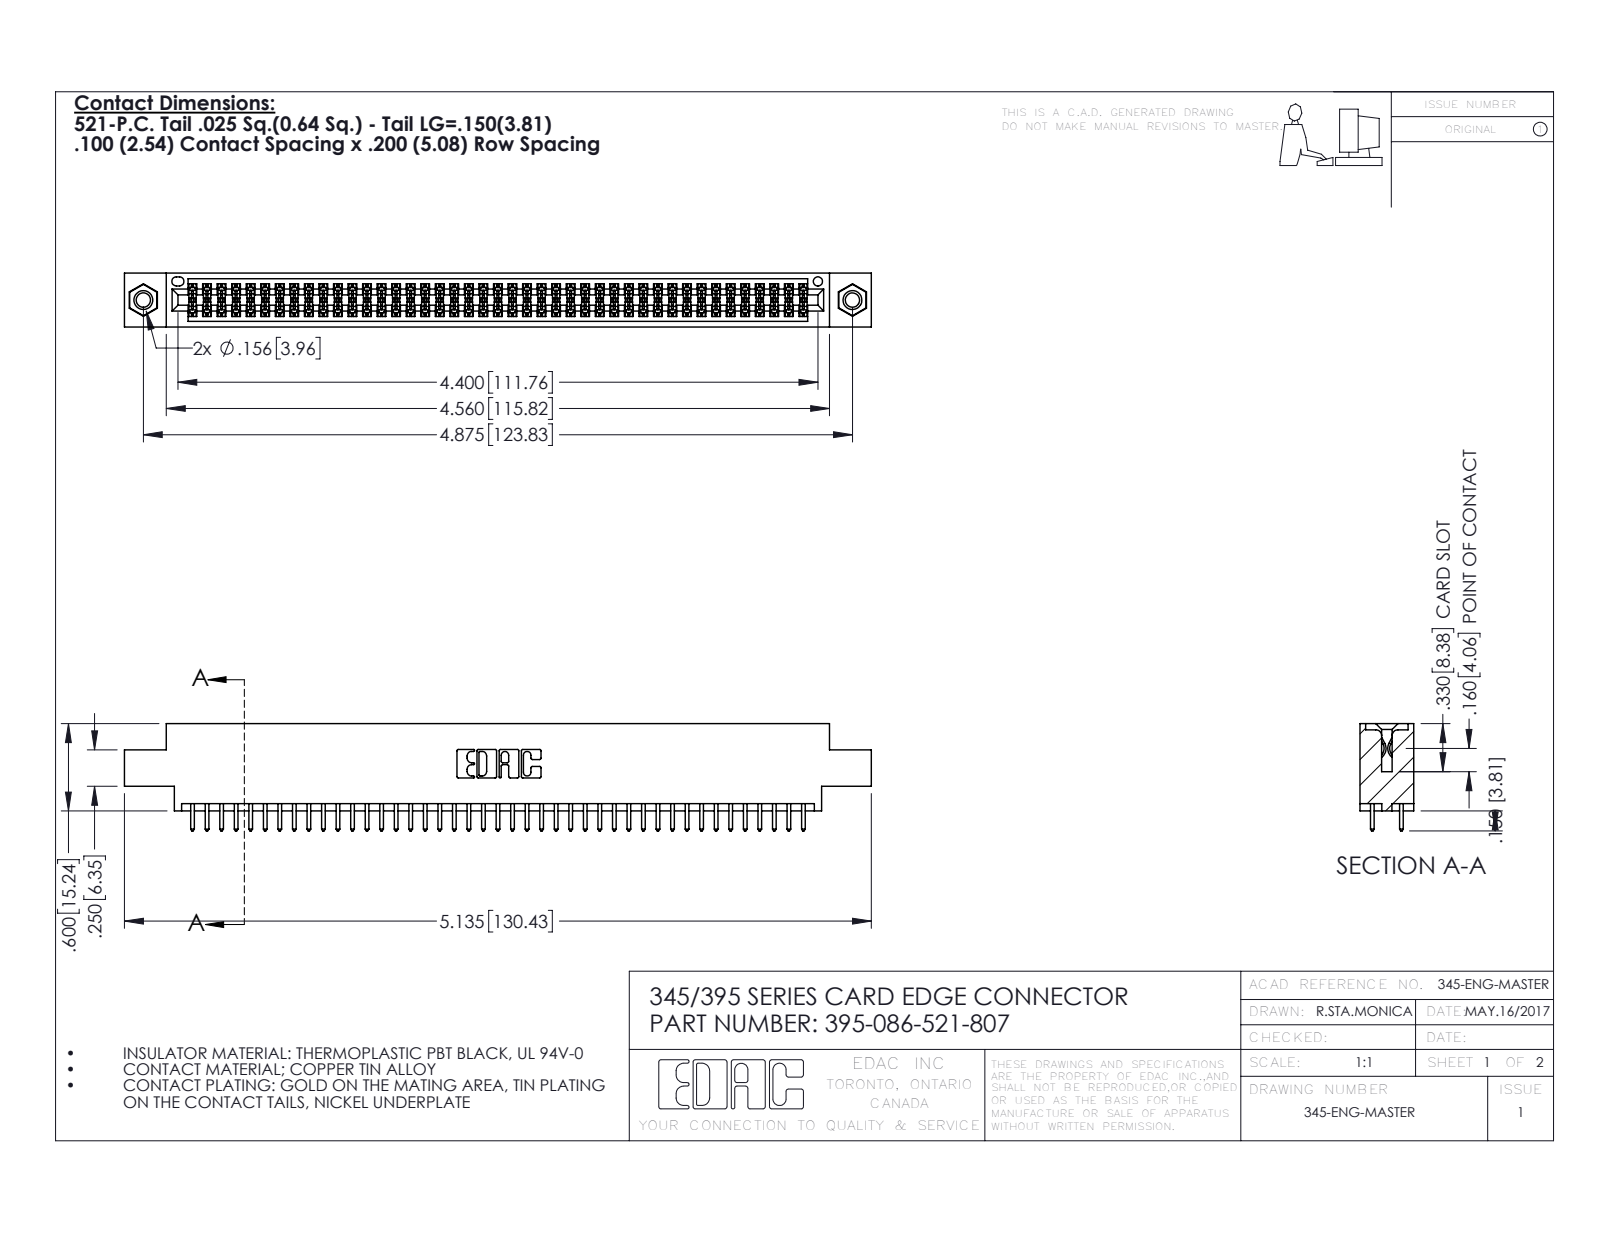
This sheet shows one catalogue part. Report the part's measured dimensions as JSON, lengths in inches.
{"part_name": "345-292-001_345-293-121; 345-250-001_345-250-005-103; 345 Part_0.170 Offset - 0.156 Dia-TI; 395-086-521-807", "step_written_by": "SolidWorks 2016 (CONFIG_CONTROL_DESIGN)", "units": "inches", "bodies": {"solids": 89, "faces": 4490, "planar": 2954, "cylindrical": 1520, "other": 16}, "overall_size": [5.135, 0.737, 0.37], "volume_in3": 0.764, "surface_area_in2": 28.62, "round_holes": [[0.098, 2], [0.125, 2], [0.156, 2], [0.064, 1]], "round_bosses_or_shafts": [[0.155, 2]], "partial_cylinders_radius": [[0.006, 129], [0.01, 86], [0.01, 22], [0.007, 6], [0.031, 6], [0.026, 3], [0.014, 2], [0.019, 2]], "face_to_face_distances": [0.072, 0.298, 0.37, 0.2, 0.098, 0.272, 0.025, 0.225, 0.175, 0.149], "hole_center_spacings": [0.27, 4.639, 4.875]}
